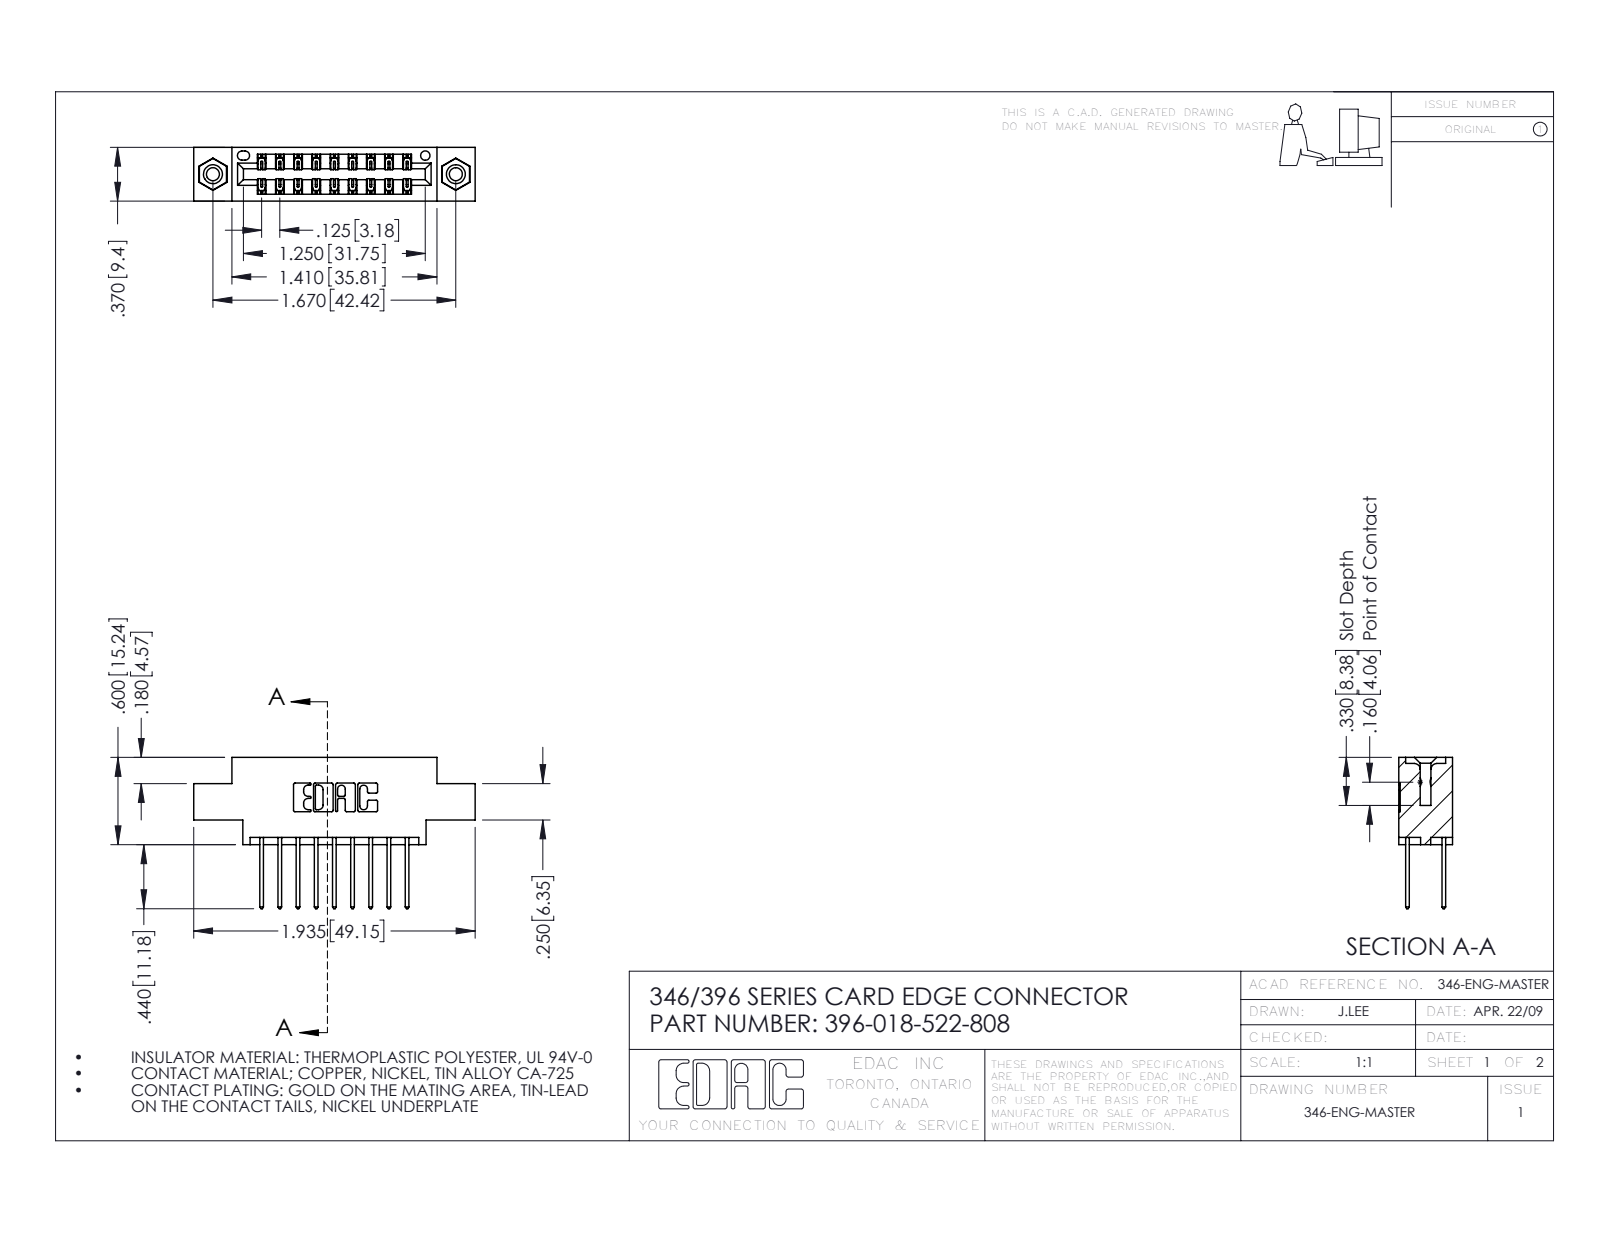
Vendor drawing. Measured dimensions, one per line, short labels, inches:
name: 396-018-522-808; 345-250-001_345-250-003-102; 346 Part_0.170 Offset - 0.156 Dia-TI; 345-292-001_345-293-122
written by: SolidWorks 2016 (CONFIG_CONTROL_DESIGN)
unit: in
bodies: 21 solids, 1122 faces (742 planar, 364 cylindrical, 16 other)
size: 1.935 × 1.04 × 0.37
volume: 0.27 in³; area: 9.257 in²
holes: 2× ⌀0.089, 2× ⌀0.125, 2× ⌀0.156, 1× ⌀0.064
bosses: 2× ⌀0.155
rounds: 27× R0.006, 22× R0.01, 18× R0.01, 6× R0.007, 6× R0.031, 3× R0.026, 2× R0.014, 2× R0.022
face distances: 0.25, 0.048, 0.322, 0.37, 0.072, 0.298, 0.025, 0.275, 0.222, 0.148
hole spacings: 0.246, 1.465, 1.67
